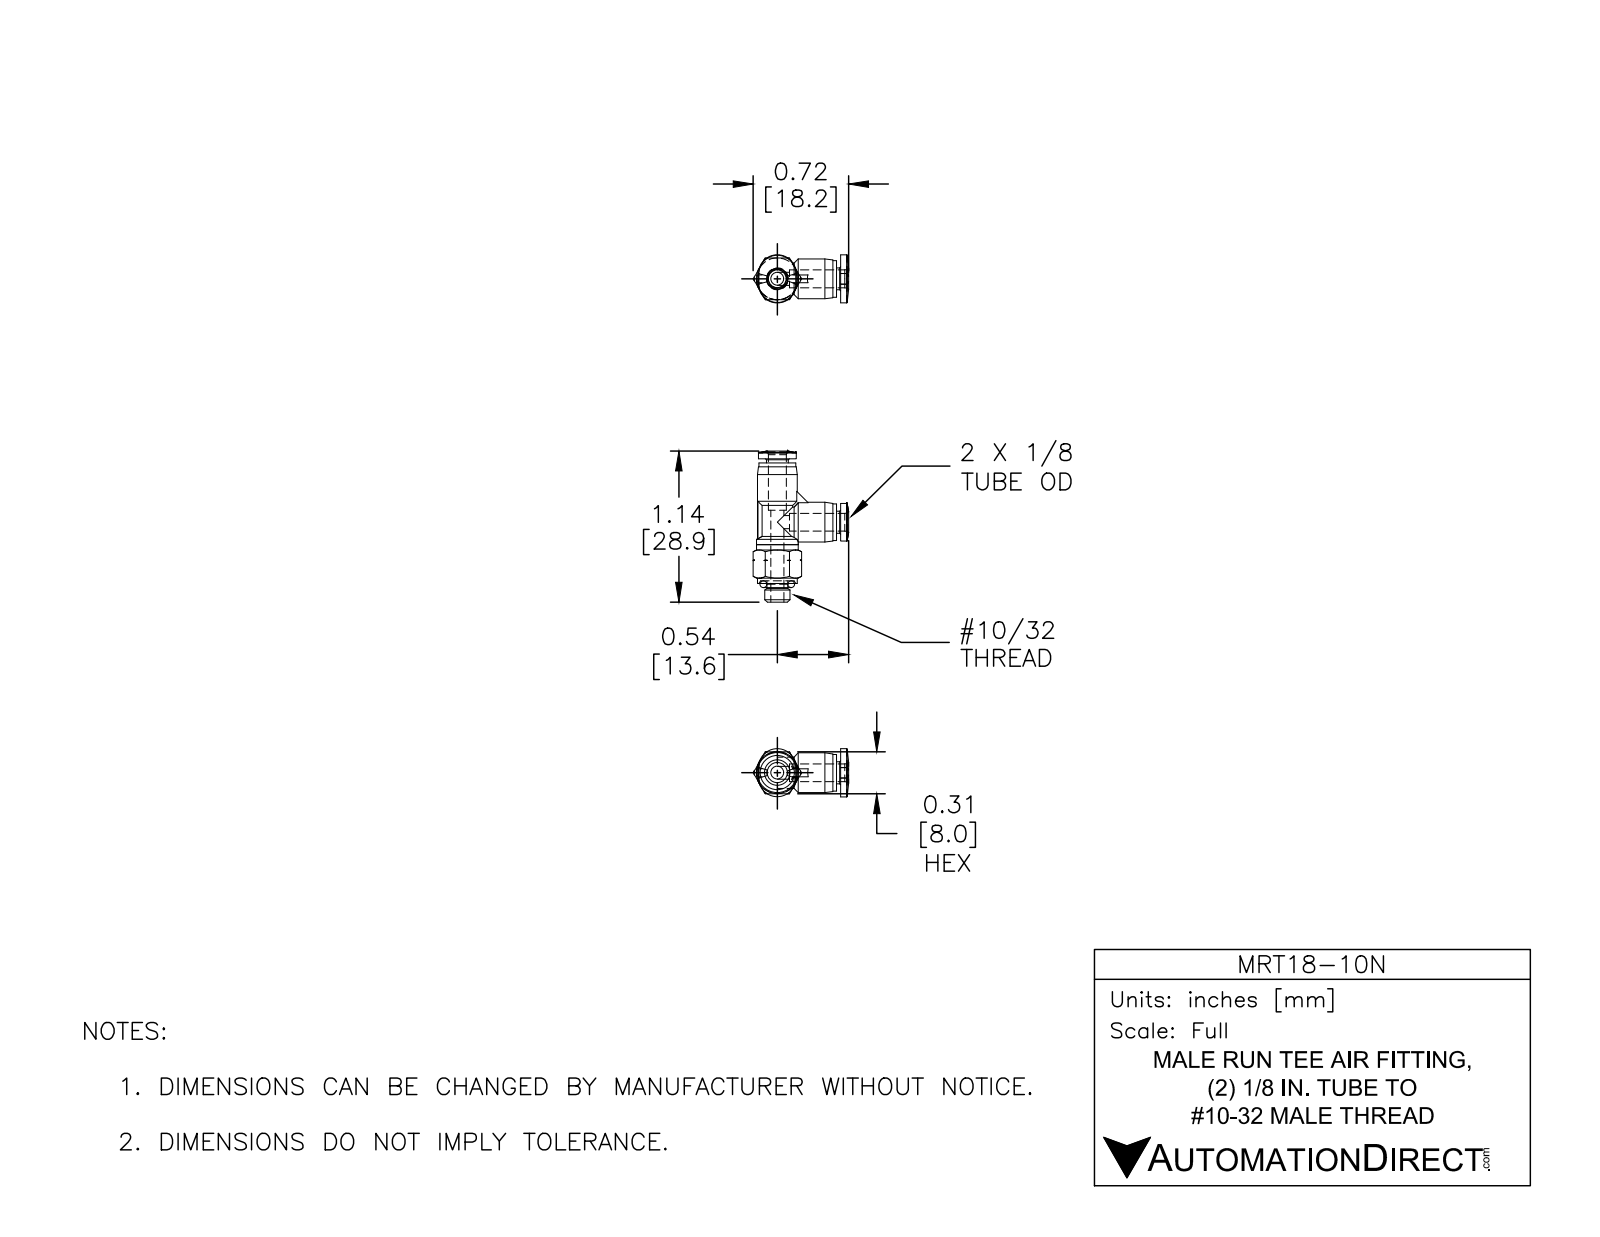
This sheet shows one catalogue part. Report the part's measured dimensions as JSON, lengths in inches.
{"part_name": "MRT18-10N", "step_written_by": "SolidWorks 2015 (CONFIG_CONTROL_DESIGN)", "units": "inches", "bodies": {"solids": 2, "faces": 158, "planar": 31, "cylindrical": 45, "other": 82}, "overall_size": [1.138, 0.717, 0.362], "volume_in3": 0.08, "surface_area_in2": 2.533, "round_holes": [[0.098, 2], [0.134, 2]], "round_bosses_or_shafts": [[0.299, 2], [0.276, 2], [0.236, 2], [0.165, 2], [0.315, 1], [0.315, 1], [0.19, 1], [0.156, 1]], "partial_cylinders_radius": [[0.142, 4]], "face_to_face_distances": [0.315, 0.031, 0.886, 0.917, 0.128, 0.187, 0.059, 0.02, 0.354, 0.386]}
